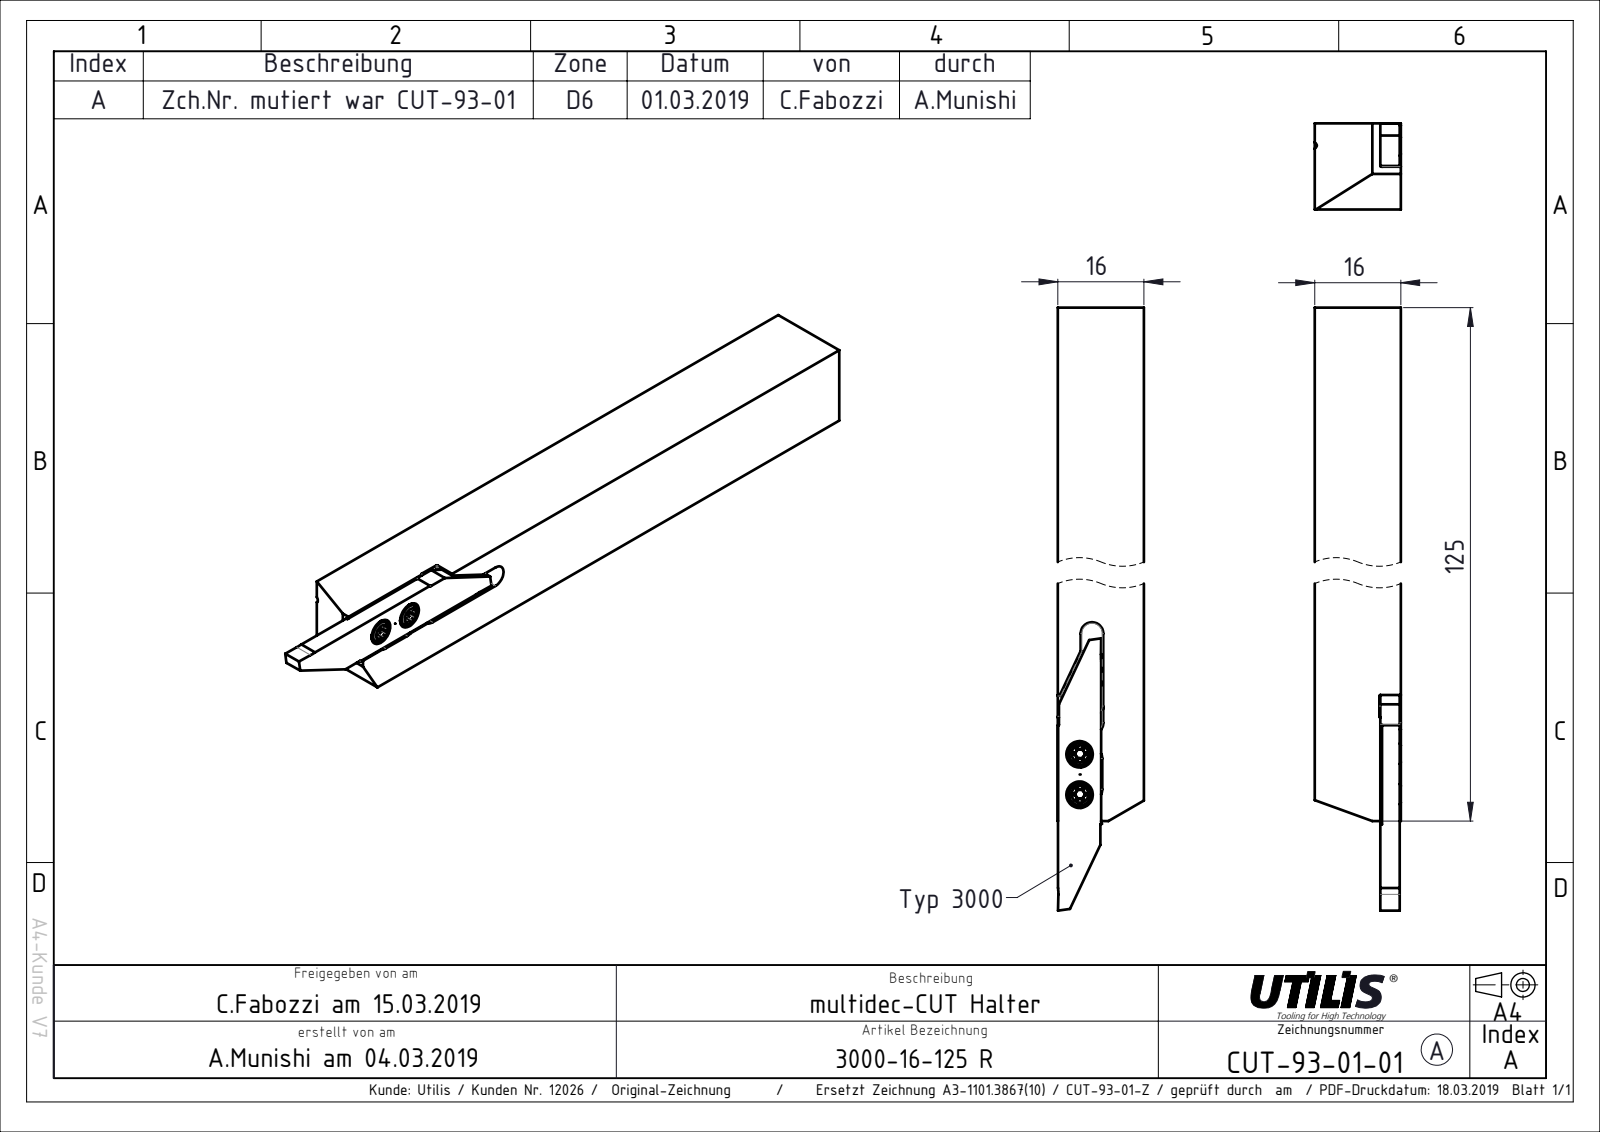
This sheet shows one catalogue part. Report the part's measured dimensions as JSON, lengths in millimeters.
{"part_name": "CUT-93-01; CUT-Vorlage 3000 R+L Lang Kunde_R-Lang; CUT-93-Kunde_01; CUT-Vorlage 3000 R+L Lang Kunde (+1 more)", "step_written_by": "SolidWorks 2015 (CONFIG_CONTROL_DESIGN)", "units": "millimeters", "bodies": {"solids": 2, "faces": 55, "planar": 36, "cylindrical": 19, "other": 0}, "overall_size": [141.5, 16, 16], "volume_mm3": 31480, "surface_area_mm2": 9704, "round_holes": [[2.5, 2], [4.9, 2]], "partial_cylinders_radius": [[2.1, 4], [0.15, 2], [10, 2]], "face_to_face_distances": [16, 3.8, 12.2, 3.6, 15.8, 8, 7.55, 0.45, 8.45, 0.4], "hole_center_spacings": [3.75, 7.5]}
